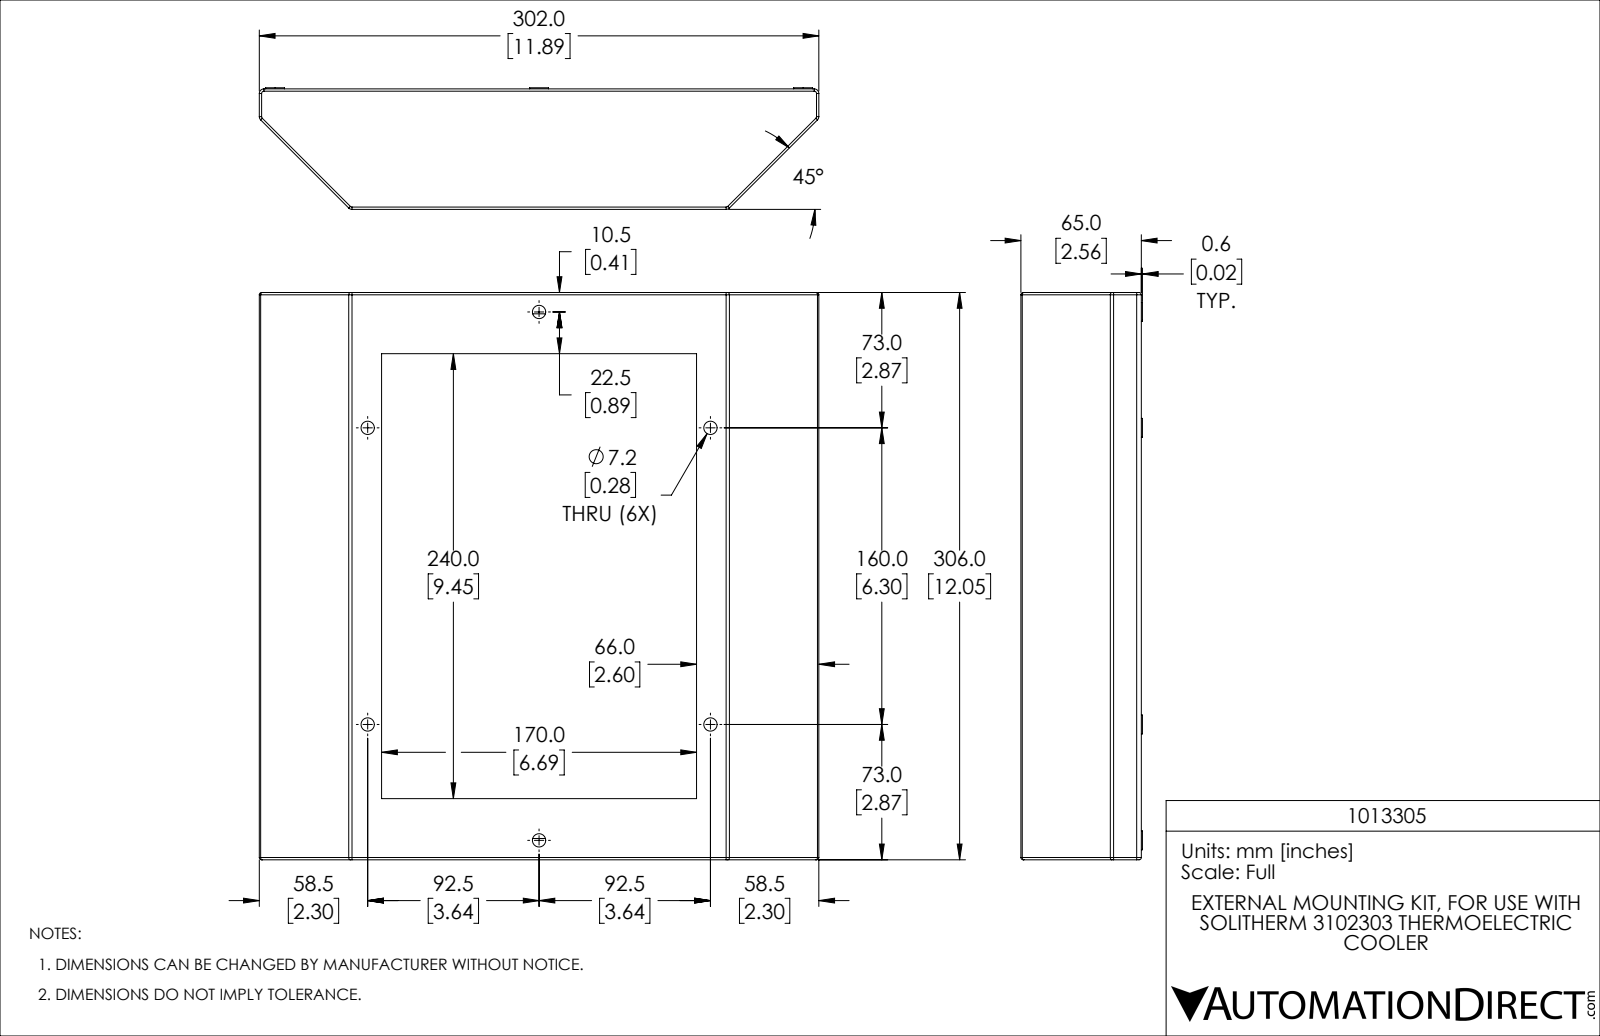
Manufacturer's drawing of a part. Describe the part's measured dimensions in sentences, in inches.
The part is named "1013305". Its 3-D file was written by "SolidWorks 2019 (AUTOMOTIVE_DESIGN)". It is 1 solid with 384 faces: 318 planar, 50 cylindrical and 16 other. Overall it measures 12.047 by 11.89 by 2.583 inches. Its volume is 60.33 cubic inches and its surface area 451.9 square inches. Round holes: 6 of diameter 0.283, 4 of diameter 0.197. Round bosses or shafts: 6 of diameter 0.402, 4 of diameter 0.35. Partial cylindrical surfaces (rounded edges, fillets, slot ends): 12 of radius 0.049, 8 of radius 0.098, 6 of radius 0.039, 2 of radius 0.175. The main face-to-face distances are 0.453, 0.059, 0.452, 11.594, 2.5, 2.559, 2.106, 2.047, 12.047, 11.142. The hole center spacings are 1.969, 4.395, 6.126, 6.299, 6.6, 9.252, 9.487, 10.402.
